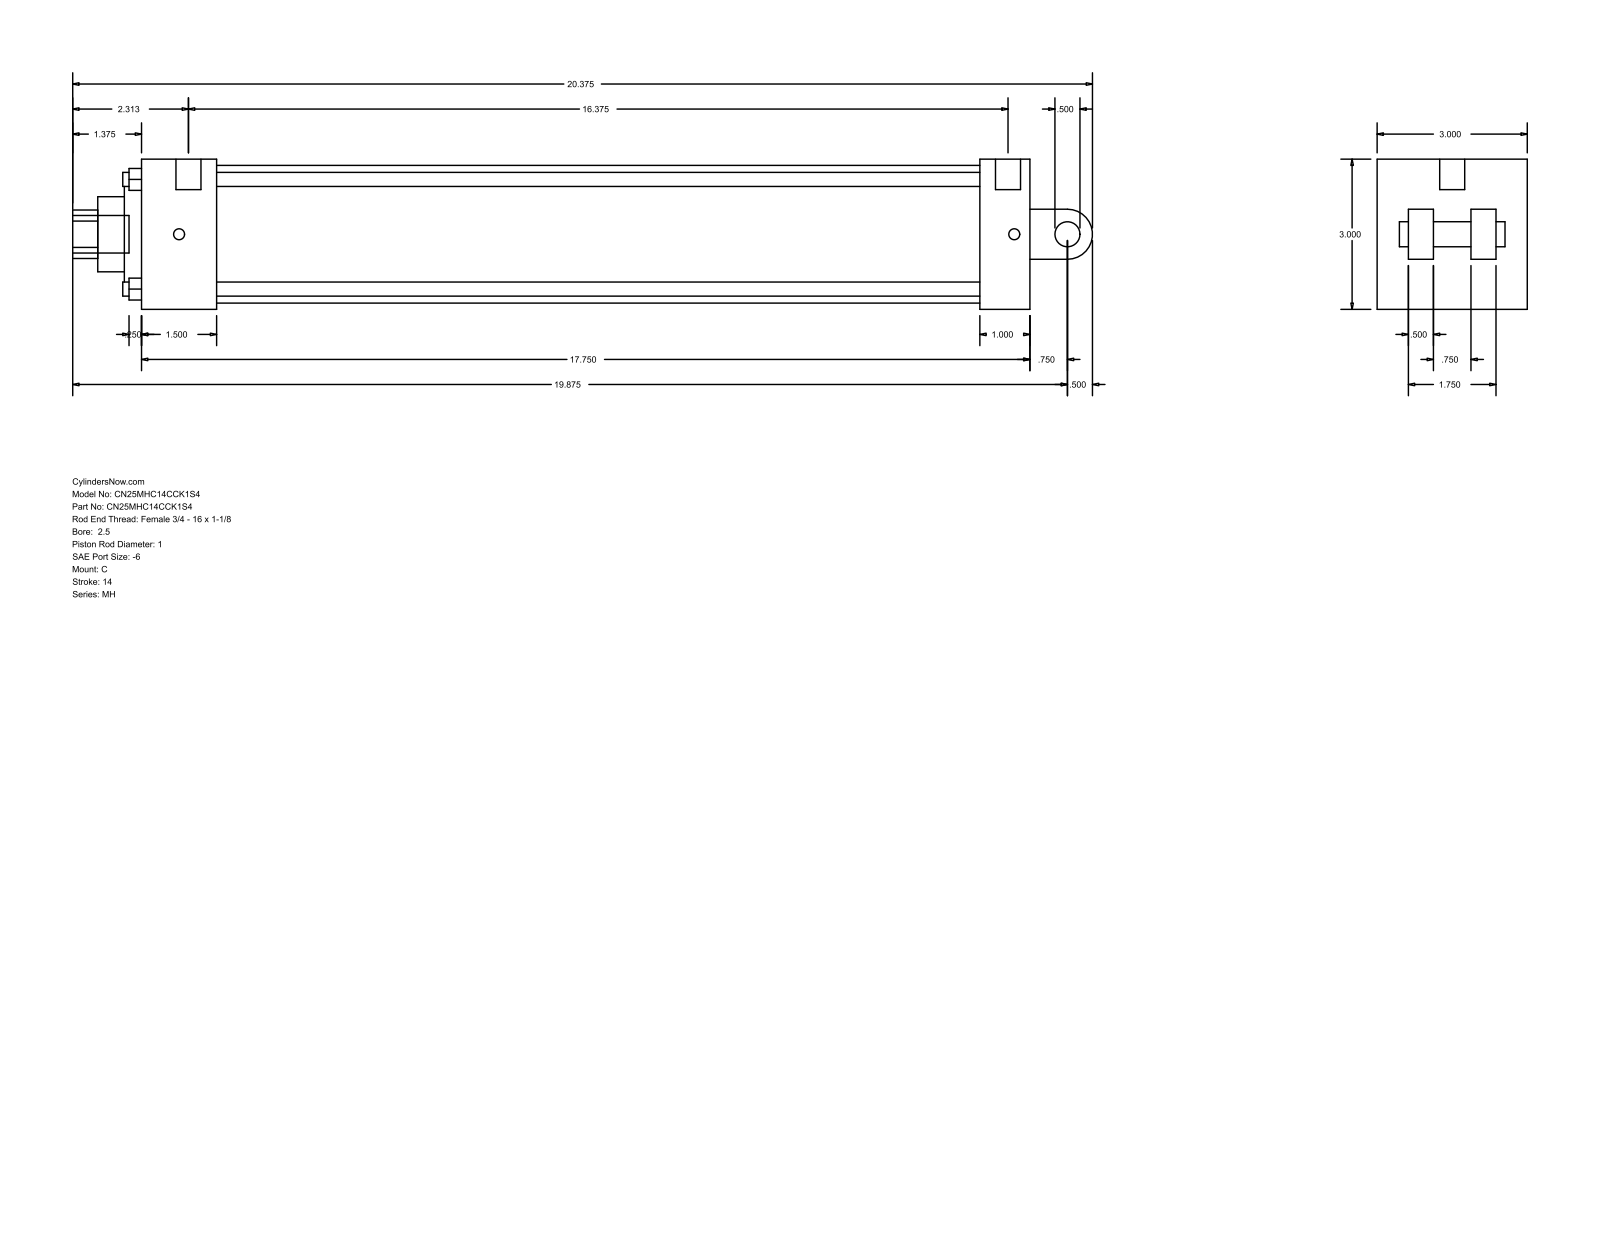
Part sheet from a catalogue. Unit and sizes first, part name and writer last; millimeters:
Units: millimetres
Overall size (bounding box): 517.52 × 76.2 × 76.2
Round holes (diameter × count): ⌀7.14 ×4, ⌀5.56 ×2, ⌀12.7 ×1, ⌀25.4 ×1, ⌀38.1 ×1, ⌀60.33 ×1, ⌀69.85 ×1
Round bosses / shafts (diameter × count): ⌀12.7 ×2, ⌀5.56 ×2, ⌀19.05 ×1
Partial cylindrical surfaces — rounded edges, fillets, slot ends (radius × count): R12.29 ×1, R12.7 ×1
Main face-to-face distances: 76.2, 450.85, 15.87, 25.39, 60.33, 425.46, 38.11, 387.35, 412.74, 12.7
Hole centre spacings: 39.33, 55.62, 78.66, 3.18
Bodies: 0 solids, 101 faces (71 planar, 30 cylindrical, 0 other)
Part name (STEP PRODUCT): MH_C__0250_1
STEP written by: GSSL Pune (CONFIG_CONTROL_DESIGN)
